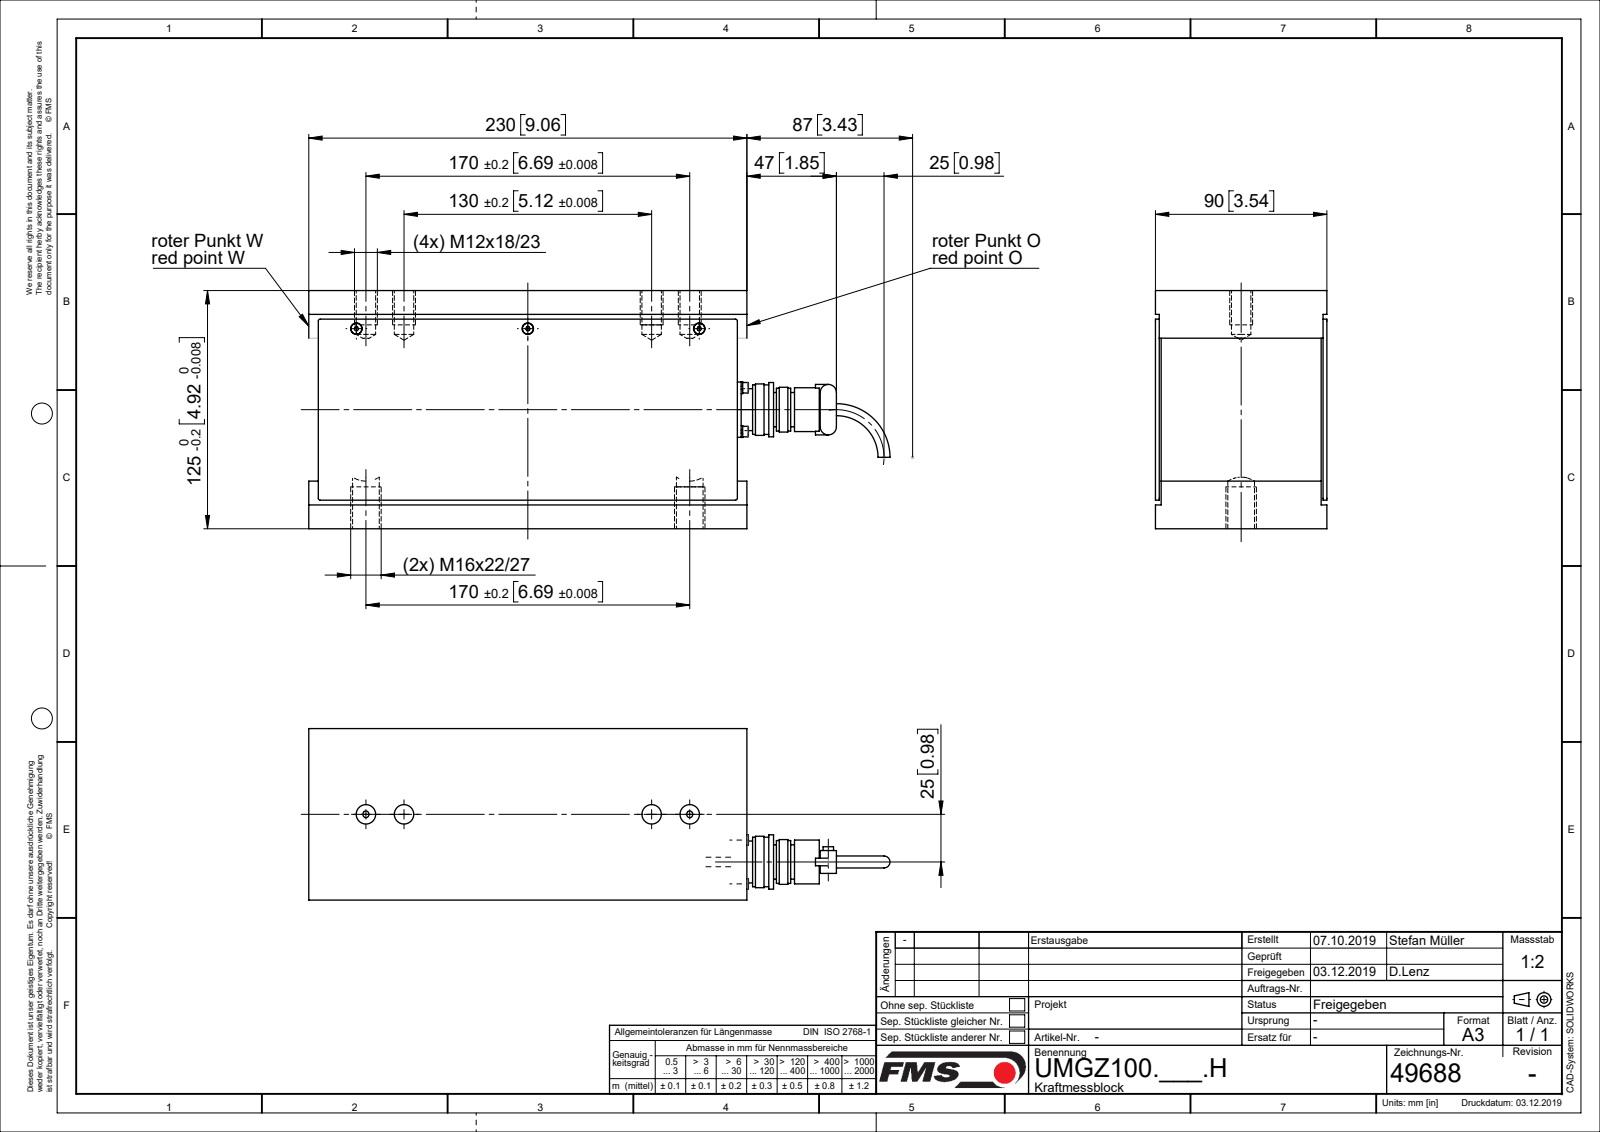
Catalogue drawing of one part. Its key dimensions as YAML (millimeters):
part_name: "U49688; U4789304; U47671; TEIL1 (+5 more)"
step_written_by: "Mechanical Desktop 2007 (CONFIG_CONTROL_DESIGN)"
units: millimeters
bodies: {solids: 18, faces: 391, planar: 133, cylindrical: 164, other: 94}
overall_size: [327.5, 125, 90]
volume: 2479000
surface_area: 230359
round_holes:
  - {diameter: 2.6, count: 7}
  - {diameter: 3.2, count: 4}
  - {diameter: 10.68, count: 4}
  - {diameter: 3.4, count: 3}
  - {diameter: 6, count: 3}
  - {diameter: 12, count: 2}
  - {diameter: 14.68, count: 2}
round_bosses_or_shafts:
  - {diameter: 3, count: 7}
  - {diameter: 6.2, count: 4}
  - {diameter: 5.5, count: 4}
  - {diameter: 2.5, count: 4}
  - {diameter: 28, count: 1}
  - {diameter: 23, count: 1}
  - {diameter: 22, count: 1}
  - {diameter: 21, count: 1}
partial_cylinders:
  - {radius: 4, count: 4}
face_to_face_distances: [2, 88, 85, 3, 1, 87, 90, 86, 125, 84]
hole_center_spacings: [23, 20, 32.53, 50, 70, 80, 90, 100]
